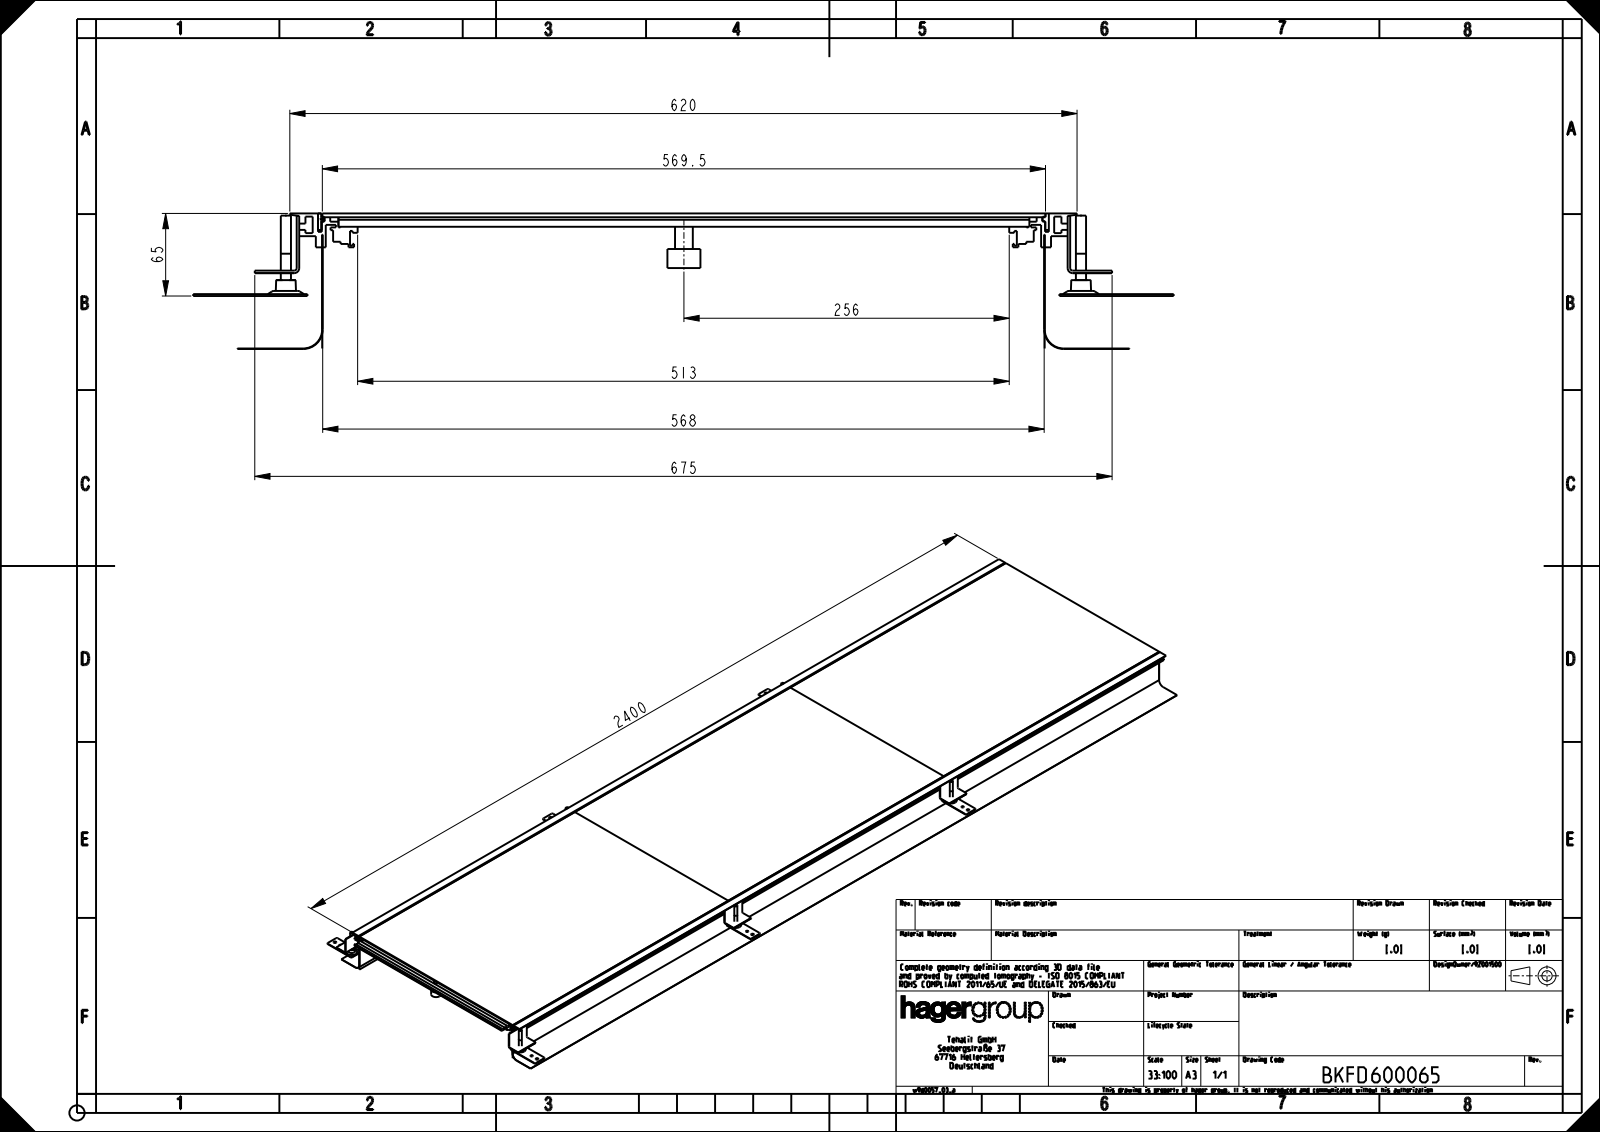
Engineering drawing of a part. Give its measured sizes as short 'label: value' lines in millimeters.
name: U05644KUN; U05650KUN; U05647KUN; U05826KUN (+8 more)
written by: CREO PARAMETRIC BY PTC INC, 2020281 (AUTOMOTIVE_DESIGN)
unit: mm
bodies: 62 solids, 1026 faces (600 planar, 354 cylindrical, 72 other)
size: 2432.5 × 772.13 × 106.7
volume: 8 936 000 mm³; area: 6 713 000 mm²
holes: 15× ⌀7, 9× ⌀8, 9× ⌀10, 6× ⌀6, 6× ⌀8.5, 6× ⌀11.5, 6× ⌀17.5, 6× ⌀23
bosses: 9× ⌀26, 9× ⌀14, 9× ⌀11.9, 6× ⌀20, 6× ⌀8
rounds: 92× R2, 24× R3, 20× R0.5, 2× R4, 2× R15, 2× R15.4
face distances: 3, 0.4, 568.55, 7.5, 6.5, 10.5, 4, 96.2, 103.7, 106.7
hole spacings: 800, 1600, 800.25, 801.1, 802.4, 1042.3, 1055.24, 1083.09
